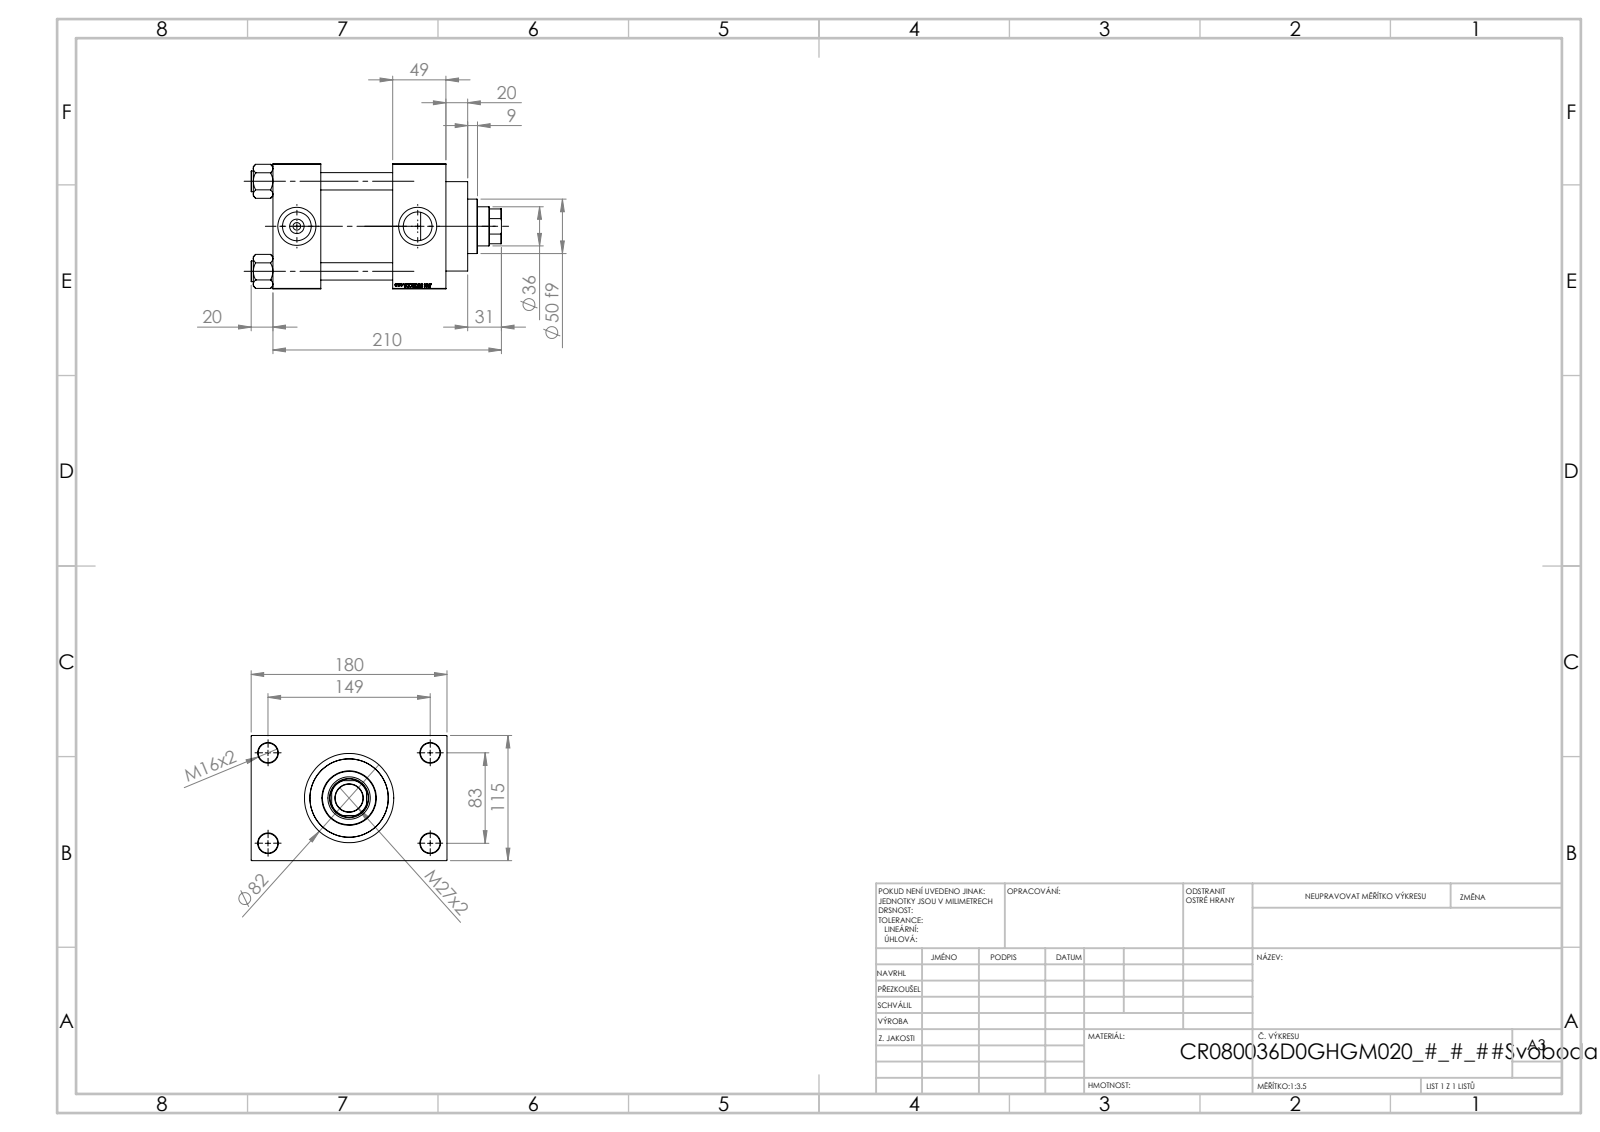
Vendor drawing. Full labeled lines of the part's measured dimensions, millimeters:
Part name (STEP PRODUCT): V215_VC_A; V215CR_D_TYCINKA; V215CR_D_Body; V215CR_VCP_D (+1 more)
STEP written by: SolidWorks 2019 (CONFIG_CONTROL_DESIGN)
Units: millimetres
Bodies: 11 solids, 1151 faces (545 planar, 88 cylindrical, 518 other)
Overall size (bounding box): 230 × 180 × 115
Volume: 1 979 000 mm³ · Surface area: 296 594 mm²
Round holes (diameter × count): ⌀16 ×4, ⌀18 ×4, ⌀7 ×2, ⌀26.44 ×2, ⌀35 ×2, ⌀25.5 ×1, ⌀36 ×1, ⌀39 ×1, ⌀61 ×1, ⌀72 ×1, ⌀80 ×1
Round bosses / shafts (diameter × count): ⌀19 ×4, ⌀86 ×1, ⌀82 ×1, ⌀50 ×1
Partial cylindrical surfaces — rounded edges, fillets, slot ends (radius × count): R17.5 ×1
Main face-to-face distances: 115, 66, 110, 49, 44, 159, 32.5, 147.5, 20, 69
Hole centre spacings: 33.15, 58.48, 82.7, 85.28, 89.24, 115.85, 142.43, 83
